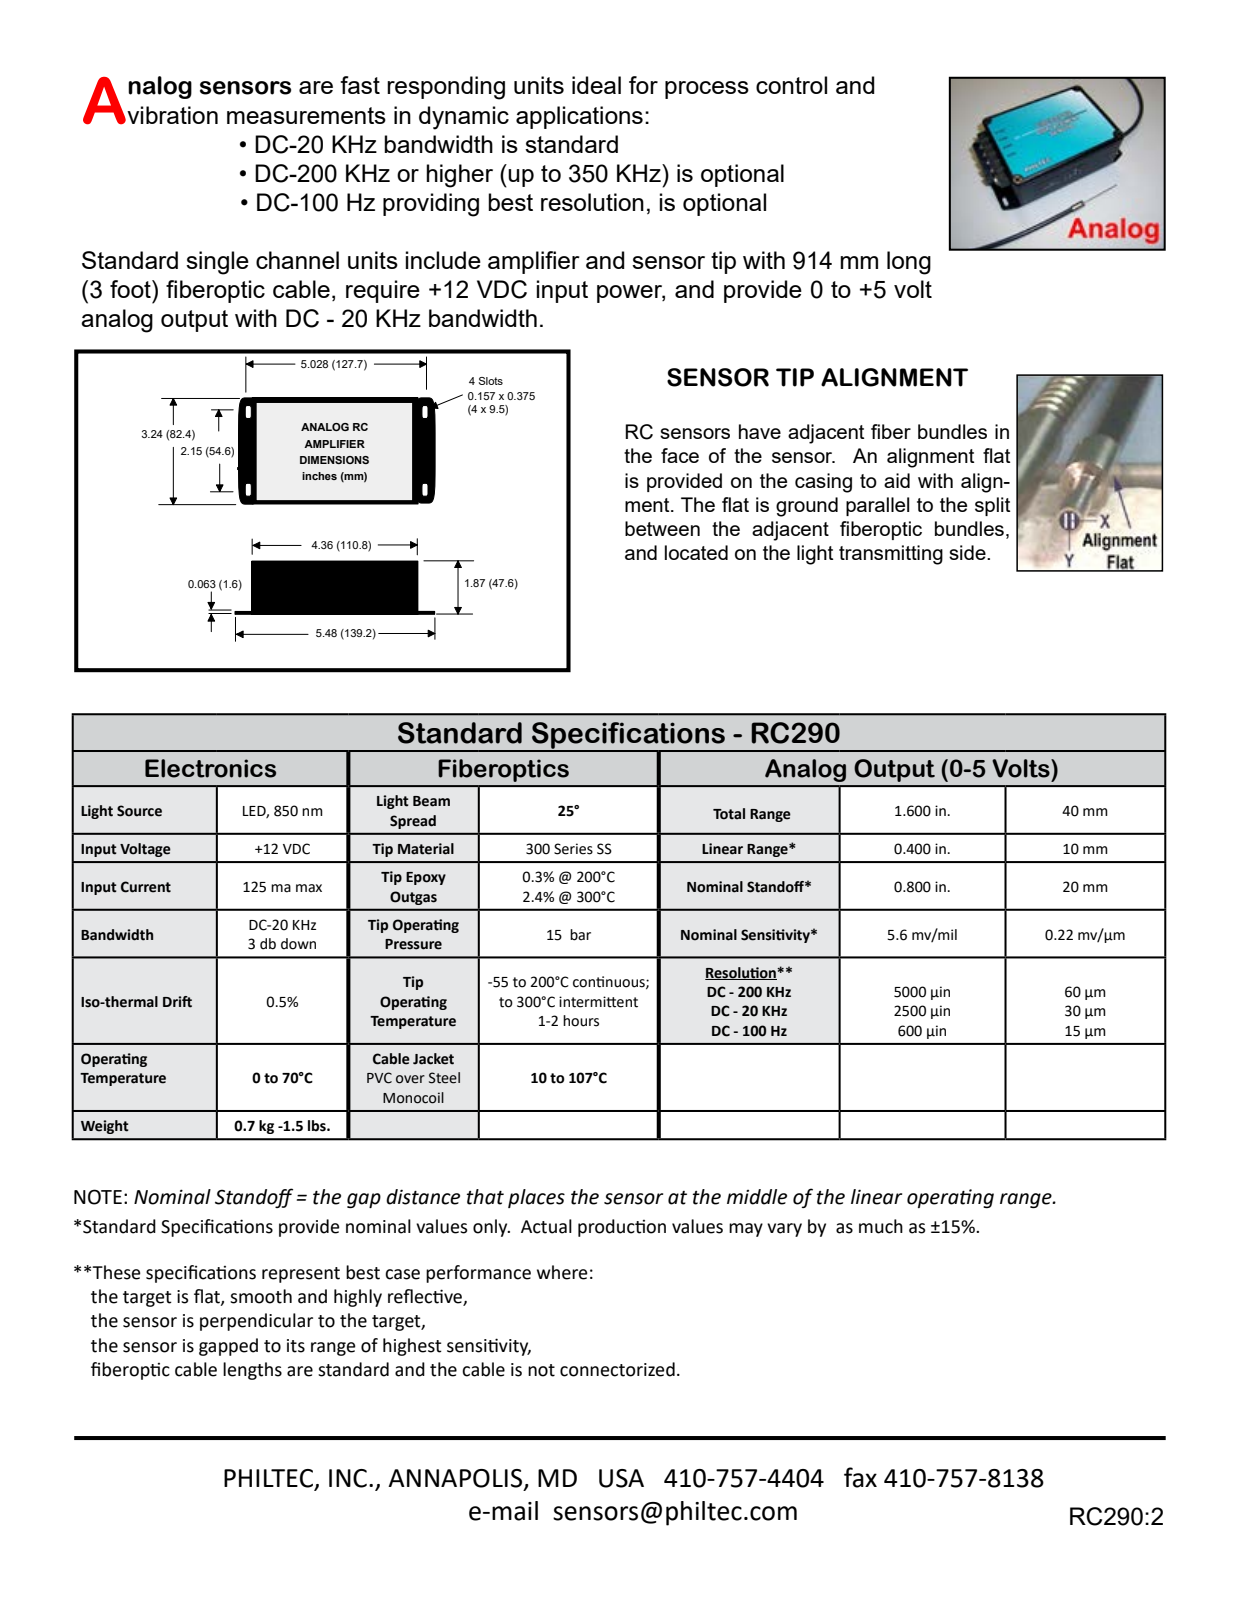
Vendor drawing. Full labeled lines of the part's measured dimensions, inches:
Part name (STEP PRODUCT): RC290
STEP written by: SolidWorks 2018 (CONFIG_CONTROL_DESIGN)
Units: inches
Bodies: 5 solids, 46 faces (22 planar, 20 cylindrical, 4 other)
Overall size (bounding box): 12.306 × 2.626 × 0.406
Volume: 1.411 in³ · Surface area: 19.27 in²
Round bosses / shafts (diameter × count): ⌀0.345 ×3, ⌀0.406 ×1, ⌀0.312 ×1, ⌀0.293 ×1
Main face-to-face distances: 0.1, 10.056, 12.306, 2.25, 12.305, 2.249, 10.806, 0.75, 1.499, 1.5
